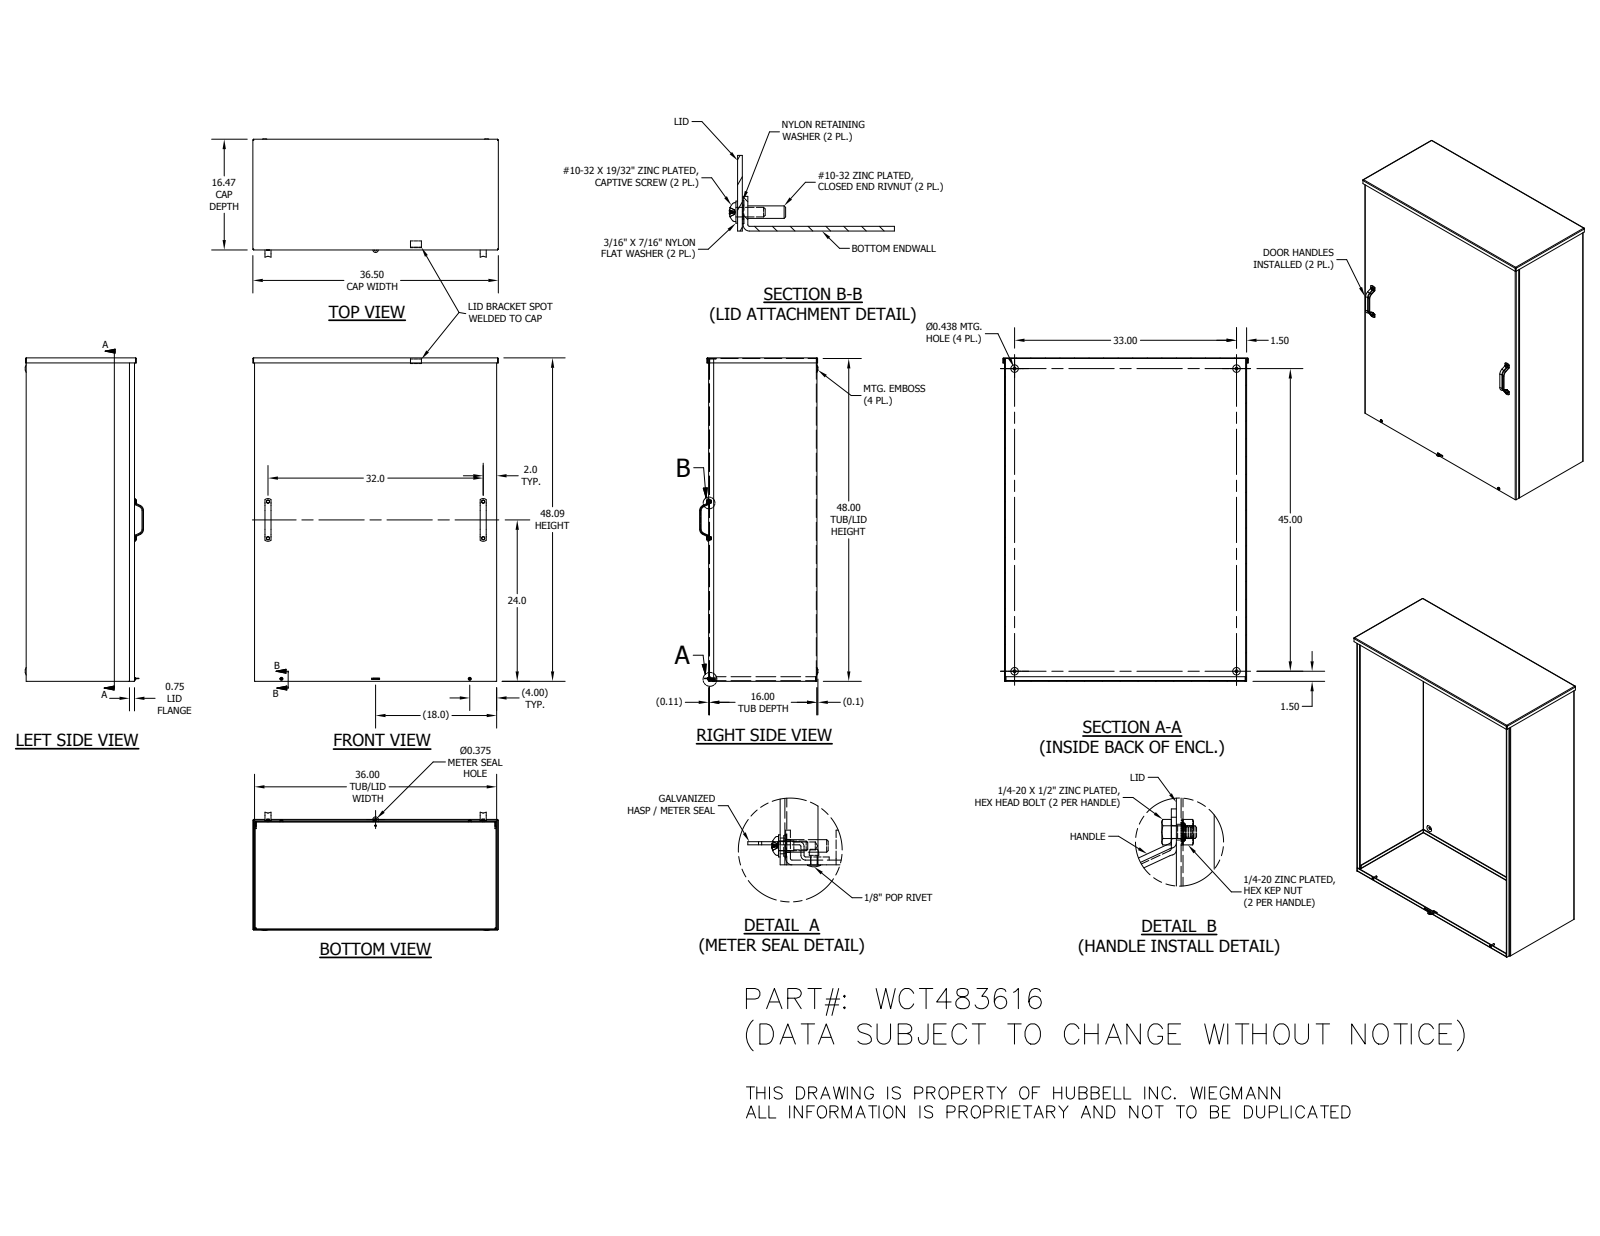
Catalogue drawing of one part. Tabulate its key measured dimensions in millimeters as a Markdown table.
| quantity | value |
| --- | --- |
| part name | WCT483616BKP; WCT3616BTM; WCT4836LID; WCT3616CAP (+8 more) |
| STEP written by | Autodesk Inventor 2014 (AUTOMOTIVE_DESIGN) |
| units | millimeters |
| bodies | 30 solids, 1094 faces (540 planar, 315 cylindrical, 239 other) |
| overall size | 1222.6 × 927.1 × 446.7 |
| volume | 9 763 000 mm³ |
| surface area | 8 251 000 mm² |
| round holes (diameter × count) | 7.94 × 6, 4.83 × 4, 6.35 × 4, 7.33 × 4, 8.51 × 4, 9.65 × 4, 11.11 × 4, 3.17 × 2, 3.96 × 2, 4.78 × 2, 4.98 × 2, 6.53 × 2 |
| round bosses / shafts (diameter × count) | 11.13 × 4, 9.52 × 4, 8.38 × 4, 7.11 × 4, 11.51 × 2, 11.11 × 2, 10.31 × 2, 9.47 × 2 |
| partial cylindrical surfaces (radius × count) | 0.51 × 96, 0.79 × 19, 3.17 × 16, 1.27 × 8, 2.54 × 8, 5.08 × 8, 4.93 × 4, 17.68 × 4 |
| main face-to-face distances | 2.38, 406.8, 409.18, 404.42, 912.02, 1219.2, 909.64, 914.4, 1221.58, 1216.82 |
| hole center spacings | 502.6, 640.69, 711.2, 775.23, 966.38, 1044.88, 812.8, 19.39 |
